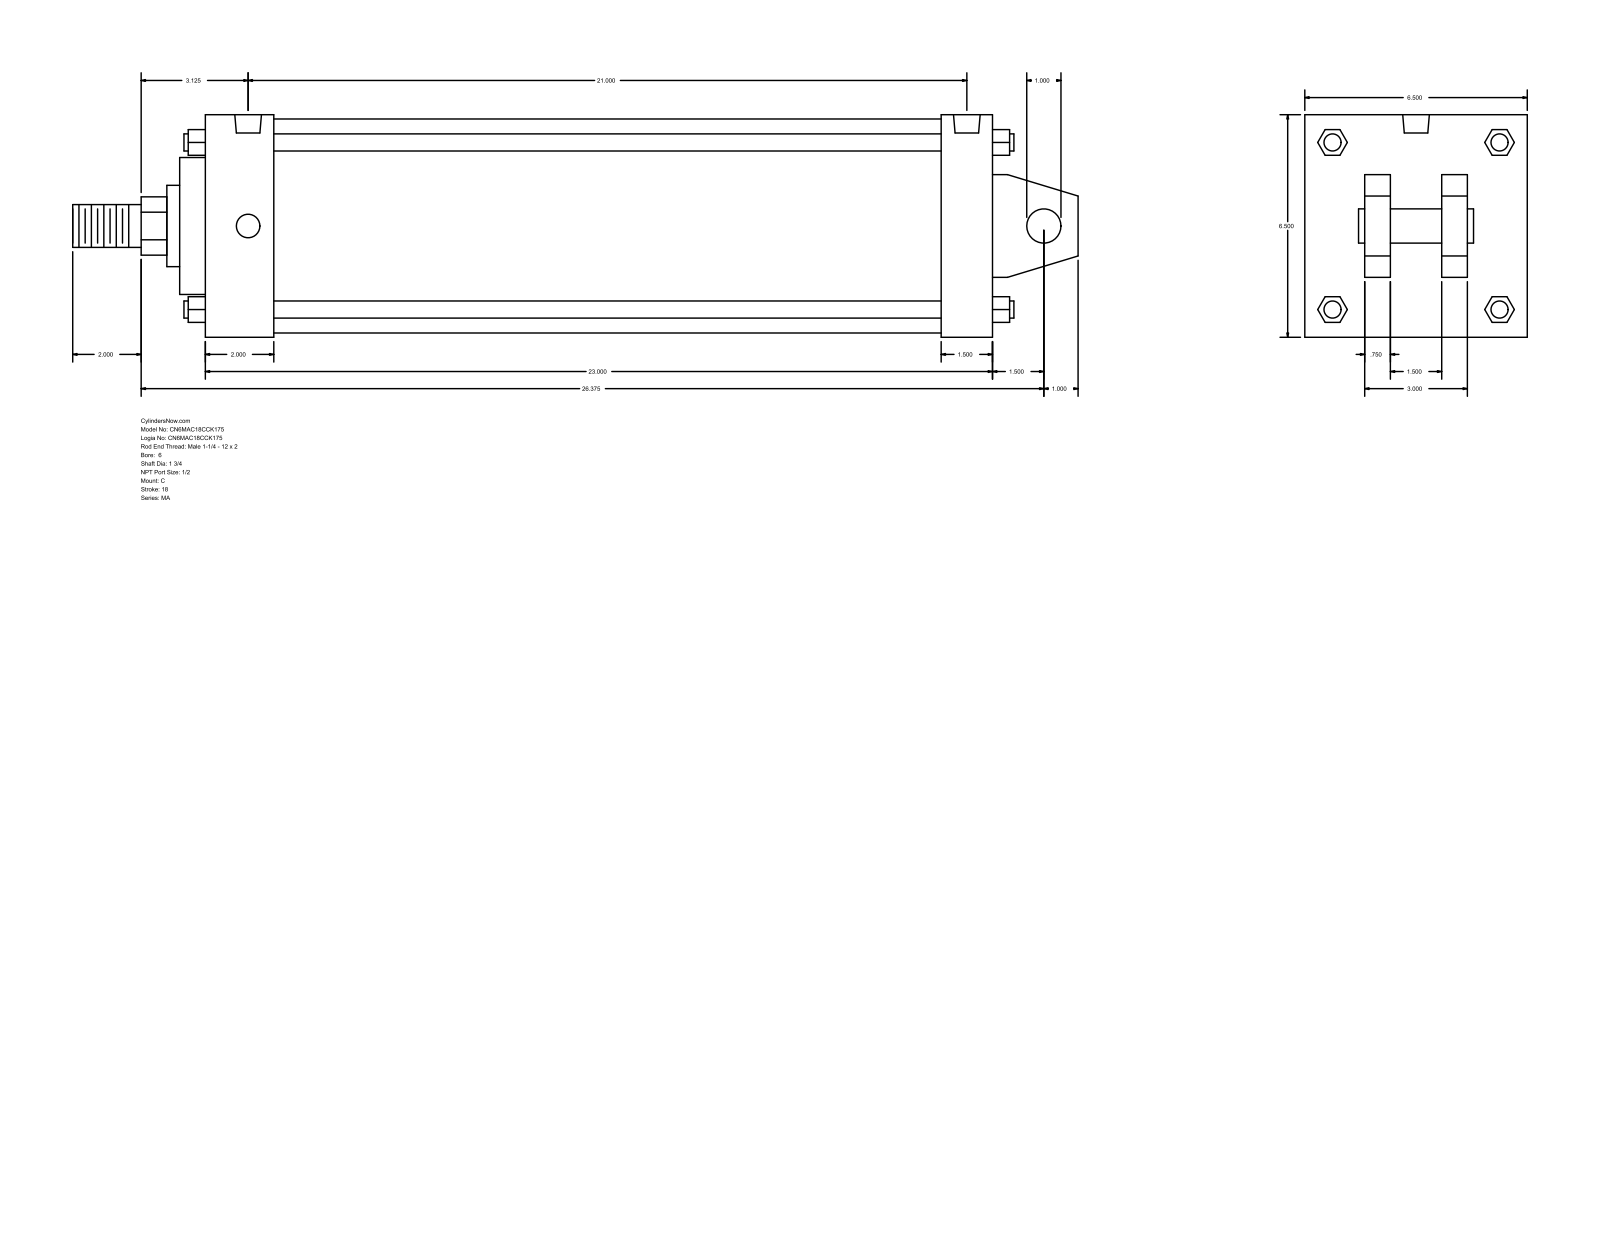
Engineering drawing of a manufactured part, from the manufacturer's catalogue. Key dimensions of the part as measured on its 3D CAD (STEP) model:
Part name (STEP PRODUCT): MA_C__0600_1.75
STEP written by: GSSL Pune (CONFIG_CONTROL_DESIGN)
Units: millimetres
Bodies: 0 solids, 141 faces (109 planar, 32 cylindrical, 0 other)
Overall size (bounding box): 746.12 × 165.1 × 165.1
Round holes (diameter × count): ⌀17.46 ×4, ⌀19.77 ×2
Round bosses / shafts (diameter × count): ⌀12.7 ×4, ⌀158.75 ×1, ⌀101.6 ×1, ⌀60.33 ×1, ⌀44.45 ×1, ⌀31.75 ×1, ⌀25.4 ×1
Partial cylindrical surfaces — rounded edges, fillets, slot ends (radius × count): R21.63 ×1
Main face-to-face distances: 165.1, 584.21, 19.05, 38.1, 63.5, 101.6, 44.45, 120.65, 57.15, 50.8
Hole centre spacings: 533.39
